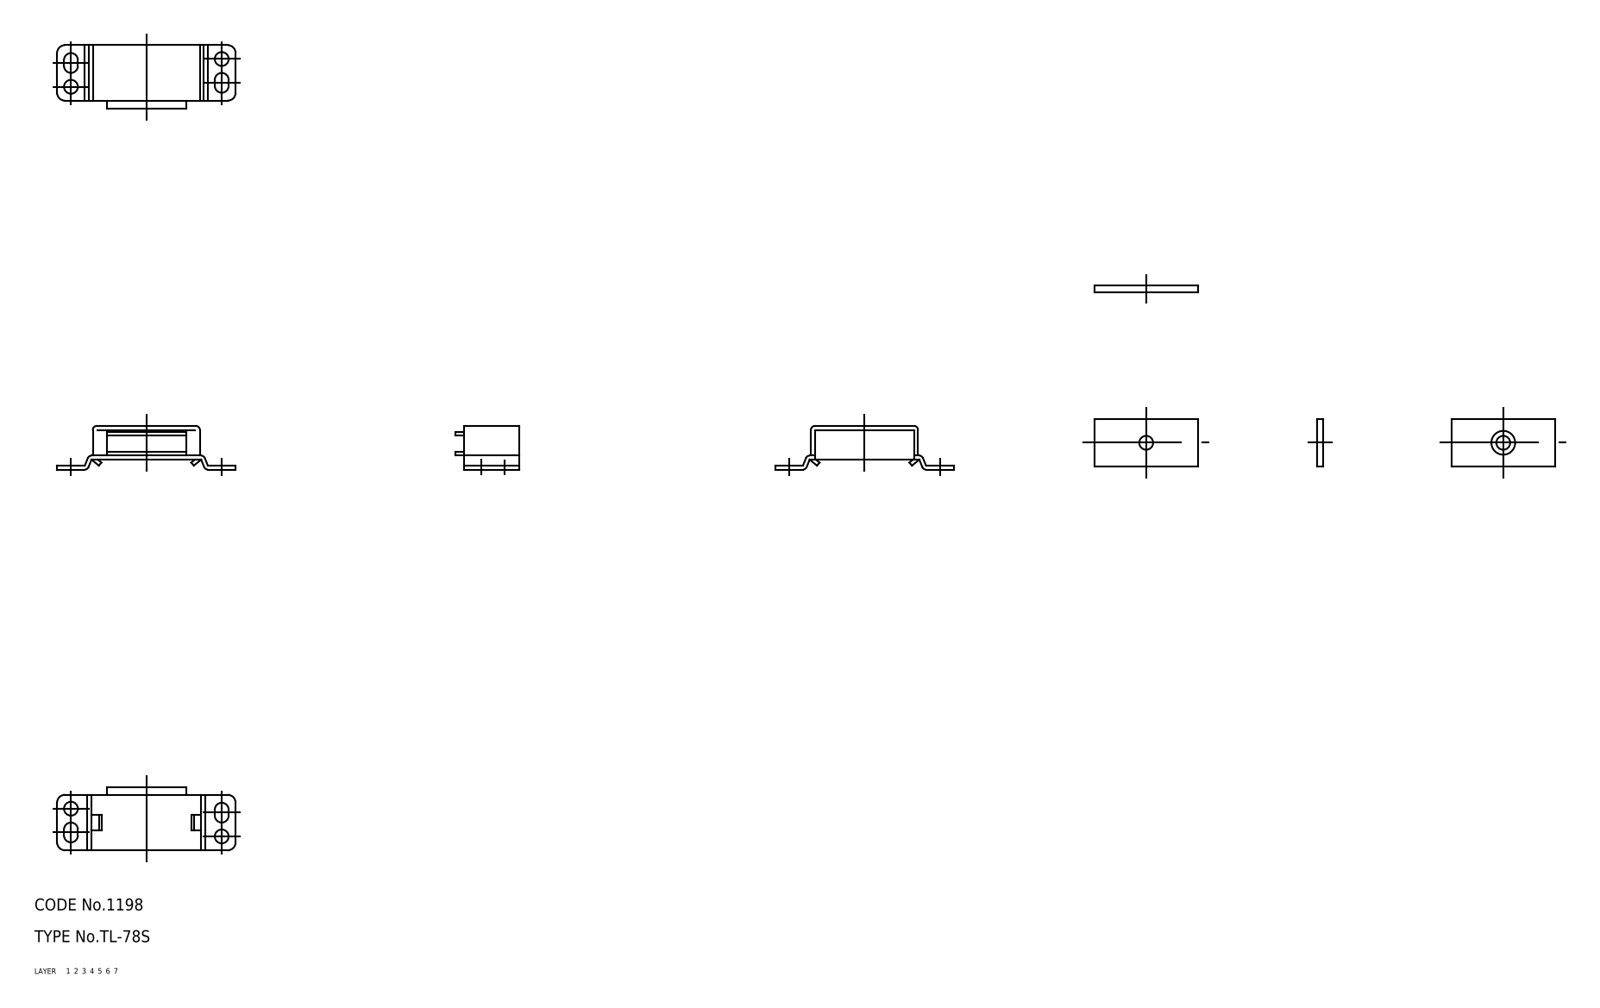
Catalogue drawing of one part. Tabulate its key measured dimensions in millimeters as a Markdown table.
| quantity | value |
| --- | --- |
| part name | 67113345; 67113358; 67113371; 67113384 (+4 more) |
| STEP written by | CADfix (AUTOMOTIVE_DESIGN) |
| units | millimeters |
| bodies | 5 solids, 120 faces (0 planar, 0 cylindrical, 120 other) |
| overall size | 45 × 31.6 × 12.75 |
| volume | 2 040 mm³ |
| surface area | 5 235 mm² |
